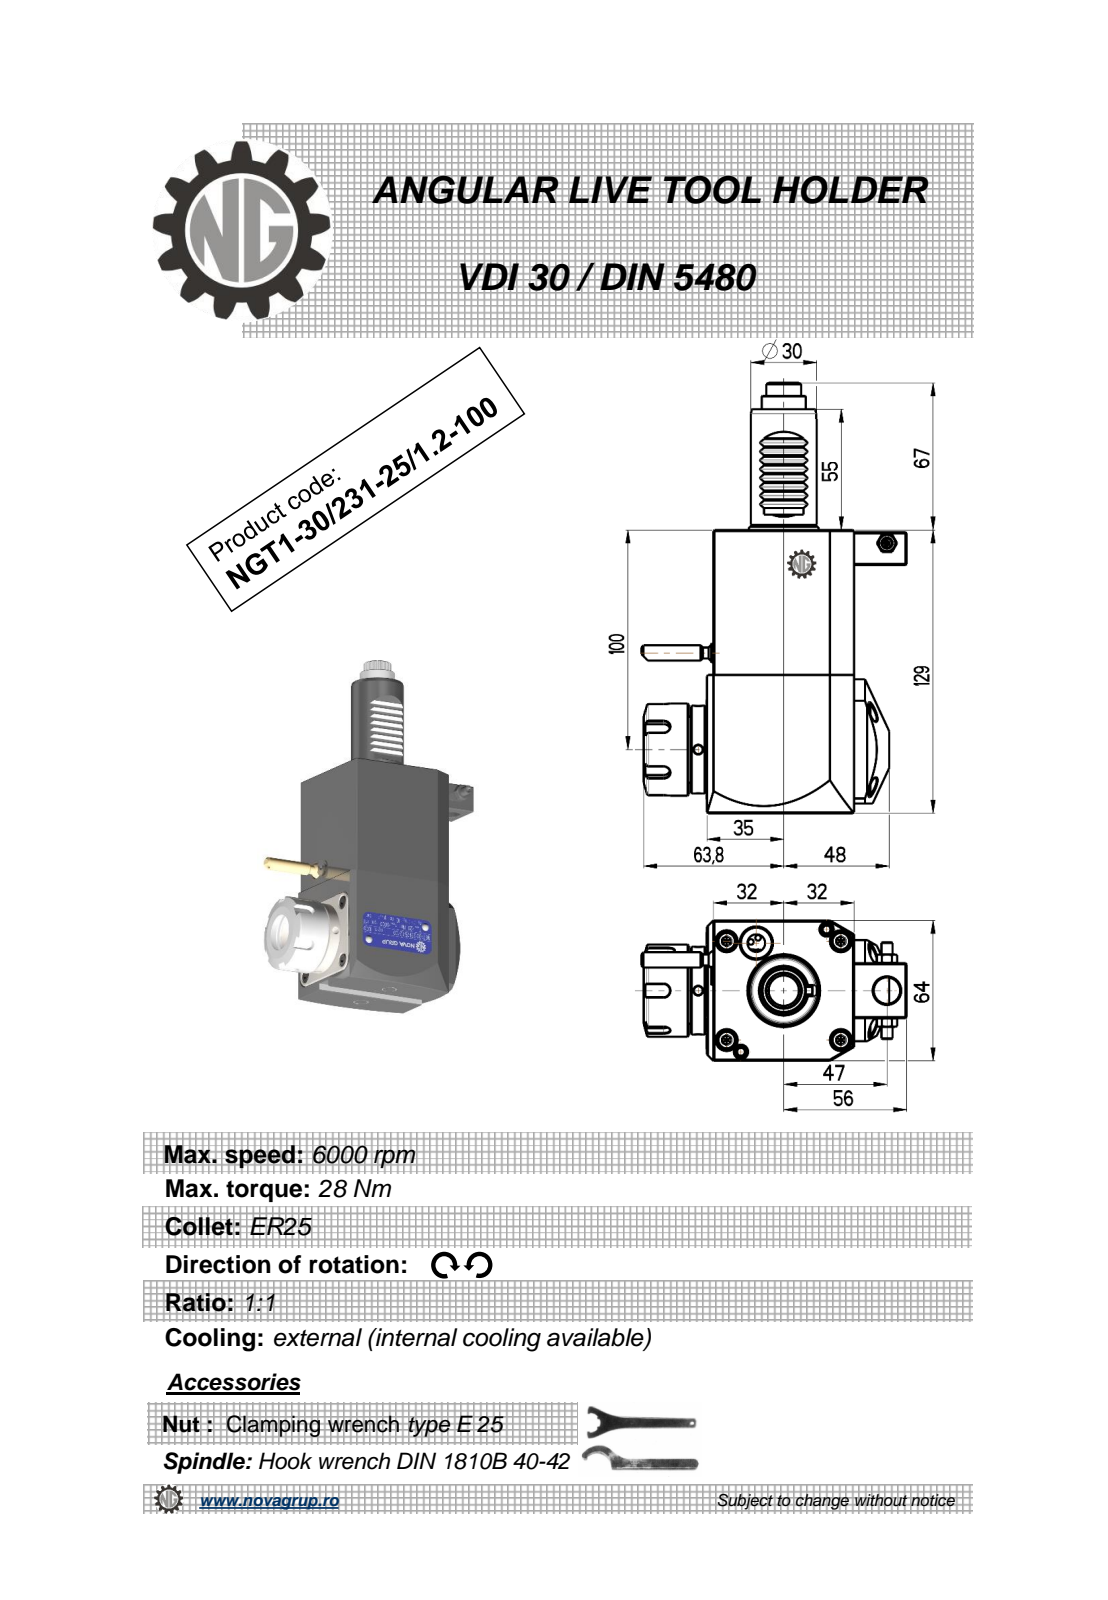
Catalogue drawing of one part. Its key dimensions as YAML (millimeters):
part_name: "NGT1_30_231_25_1_2_100"
step_written_by: "PRO/ENGINEER BY PARAMETRIC TECHNOLOGY CORPORATION, 2010280 (CONFIG_CONTROL_DESIGN)"
units: millimeters
bodies: {solids: 1, faces: 510, planar: 188, cylindrical: 161, other: 161}
overall_size: [196, 120.88, 65.6]
volume: 636542
surface_area: 58374
round_holes:
  - {diameter: 4, count: 2}
  - {diameter: 2.5, count: 1}
  - {diameter: 3, count: 1}
  - {diameter: 4.2, count: 1}
  - {diameter: 9.5, count: 1}
  - {diameter: 12, count: 1}
  - {diameter: 20.3, count: 1}
round_bosses_or_shafts:
  - {diameter: 8.96, count: 2}
  - {diameter: 5, count: 2}
  - {diameter: 42, count: 1}
  - {diameter: 40, count: 1}
  - {diameter: 33, count: 1}
  - {diameter: 30, count: 1}
  - {diameter: 20, count: 1}
  - {diameter: 7, count: 1}
partial_cylinders:
  - {radius: 1.98, count: 36}
  - {radius: 0.26, count: 12}
  - {radius: 0.3, count: 8}
  - {radius: 3, count: 5}
  - {radius: 3.5, count: 4}
  - {radius: 160, count: 2}
  - {radius: 7.08, count: 1}
  - {radius: 7.92, count: 1}
face_to_face_distances: [64, 129, 3.2, 67.2, 67, 3, 0.5, 55, 16, 4]
hole_center_spacings: [46.17, 49.52, 85.95, 91.5, 127.37]
